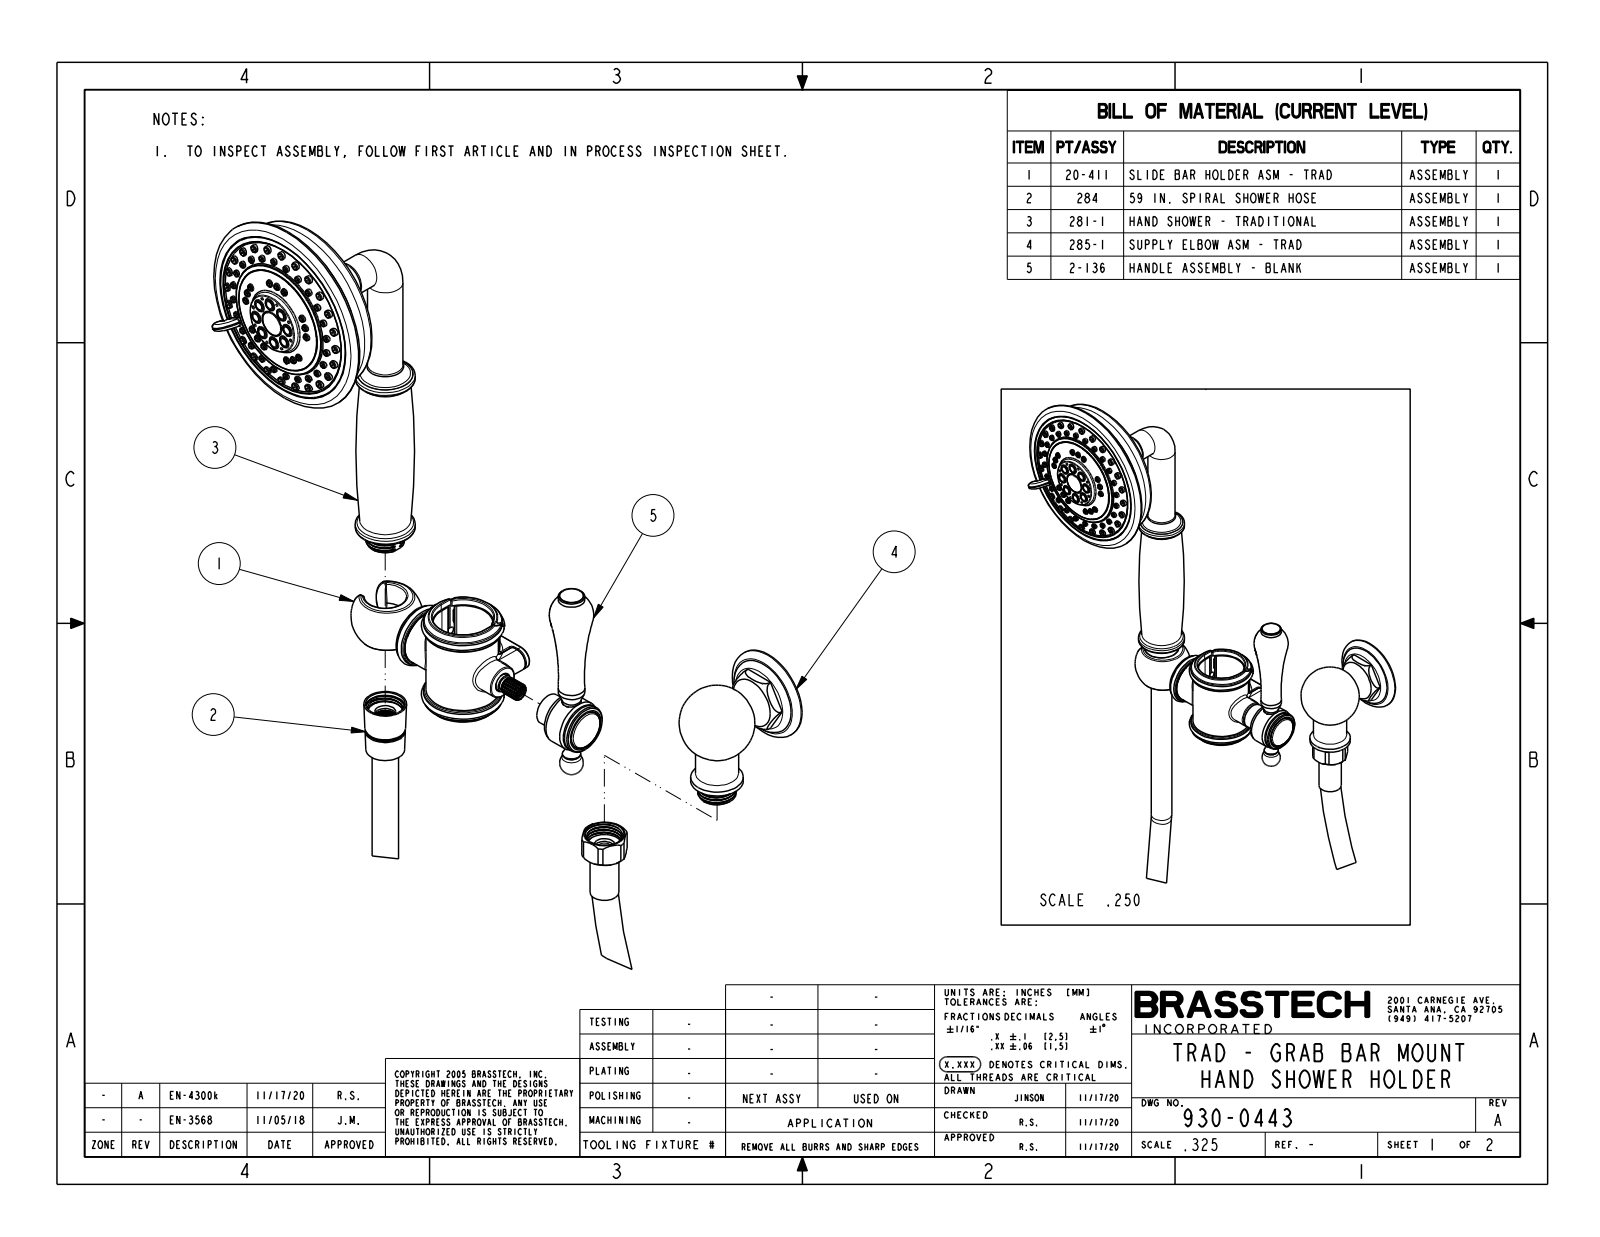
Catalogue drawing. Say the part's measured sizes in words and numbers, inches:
The part is named "930-0443". Its 3-D file was written by "CREO PARAMETRIC BY PTC INC, 2018400 (CONFIG_CONTROL_DESIGN)". It is 2 solids with 1495 faces: 196 planar, 345 cylindrical and 954 other. Overall it measures 29.637 by 15.302 by 5.533 inches. Its volume is 44.03 cubic inches and its surface area 246.3 square inches. Round holes: 8 of diameter 0.059, 1 of diameter 0.193, 1 of diameter 0.41, 1 of diameter 0.855, 1 of diameter 1.08, 1 of diameter 1.265, 1 of diameter 1.3, 1 of diameter 1.4. Round bosses or shafts: 39 of diameter 0.142, 23 of diameter 0.165, 3 of diameter 0.56, 2 of diameter 0.75, 1 of diameter 3.81, 1 of diameter 3.24, 1 of diameter 2.323, 1 of diameter 2. Partial cylindrical surfaces (rounded edges, fillets, slot ends): 44 of radius 0.02, 8 of radius 0.06, 4 of radius 0.02, 4 of radius 0.03, 2 of radius 0.033, 2 of radius 0.25, 1 of radius 0.08, 1 of radius 0.122. The main face-to-face distances are 0.02, 1.175, 1.165, 1.28, 0.5, 0.017, 1.283, 1.263, 0.25, 1.3. The hole center spacings are 0.443, 0.819, 1.069, 1.157, 0.443, 1.07, 0.818, 0.819.
